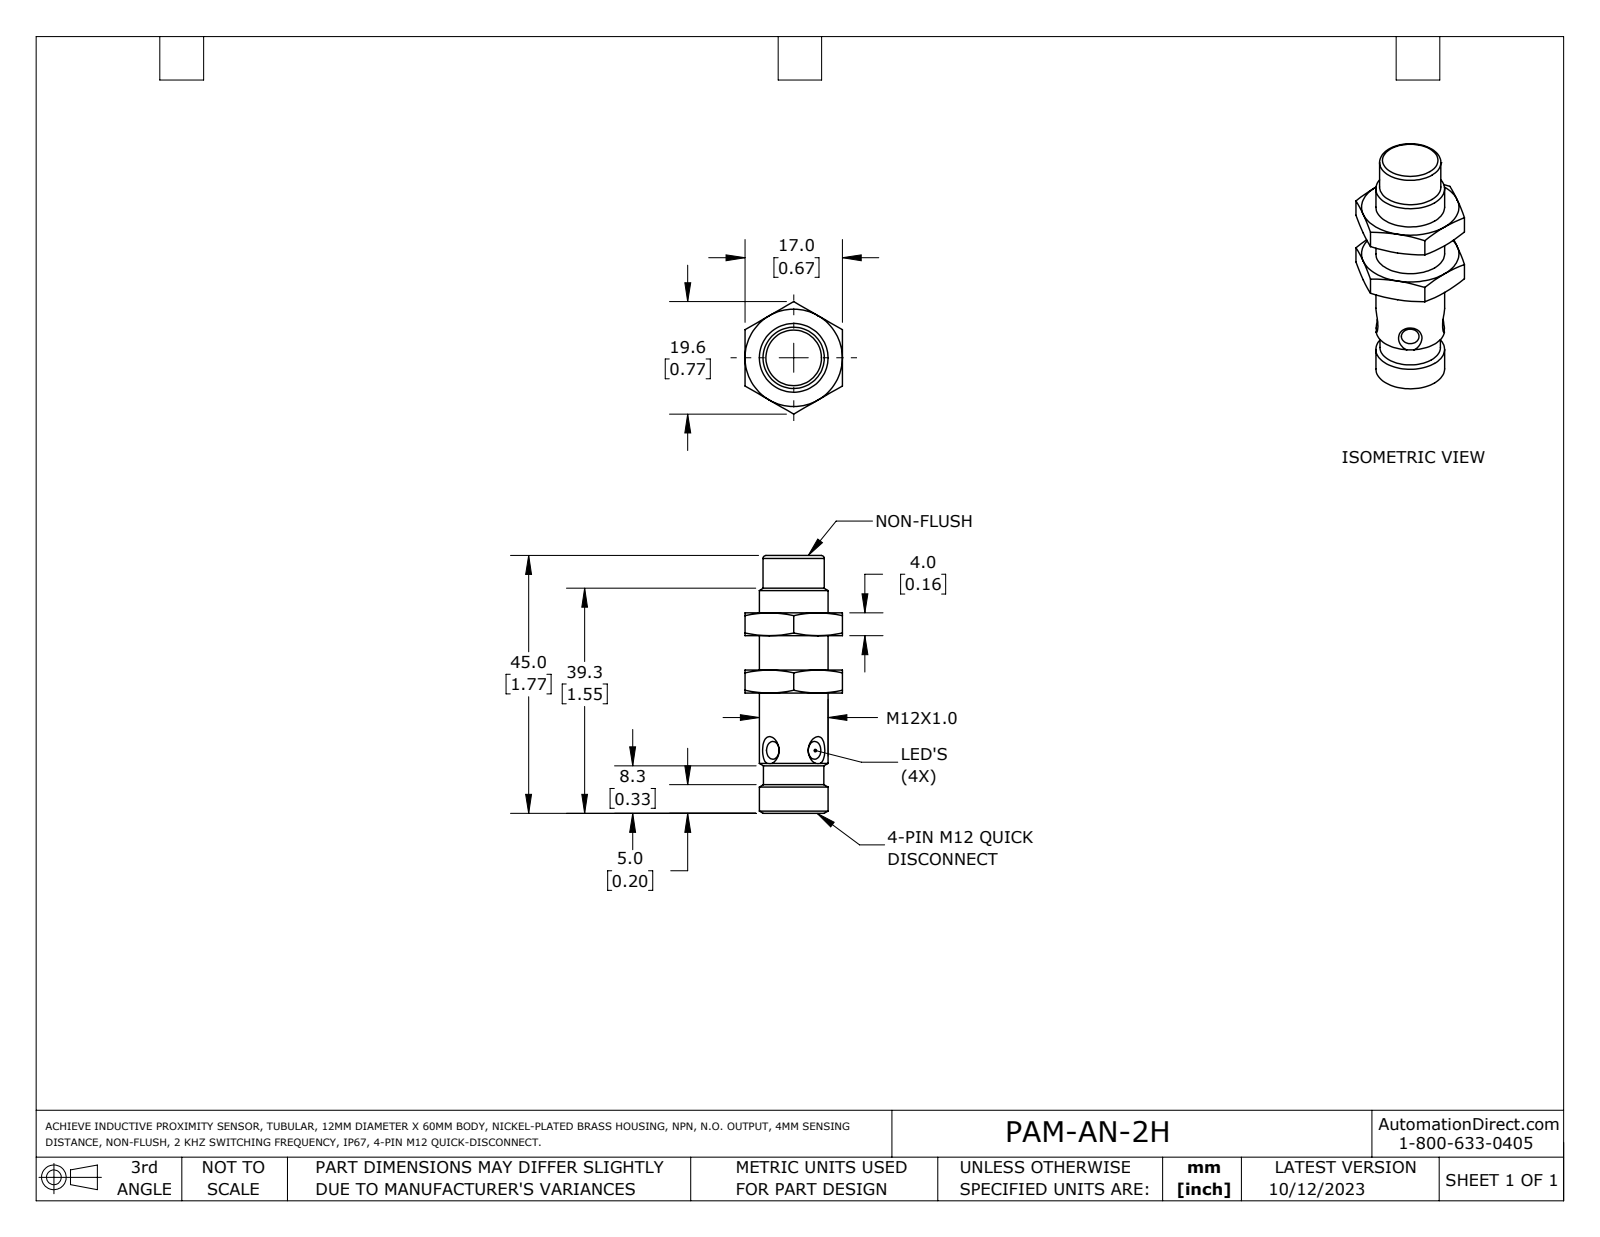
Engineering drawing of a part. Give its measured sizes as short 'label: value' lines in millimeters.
name: PAM-AN-2H
written by: SolidWorks 2023 (AUTOMOTIVE_DESIGN)
unit: mm
bodies: 3 solids, 95 faces (40 planar, 14 cylindrical, 41 other)
size: 45 × 19.6 × 17
volume: 5 420 mm³; area: 3 544 mm²
holes: 1× ⌀2.4, 1× ⌀8.5, 1× ⌀12
bosses: 4× ⌀1, 1× ⌀10.7, 1× ⌀10.5
rounds: 2× R0.6
face distances: 10, 4, 17, 14, 6, 24, 20, 12.3, 16.3, 22.3
